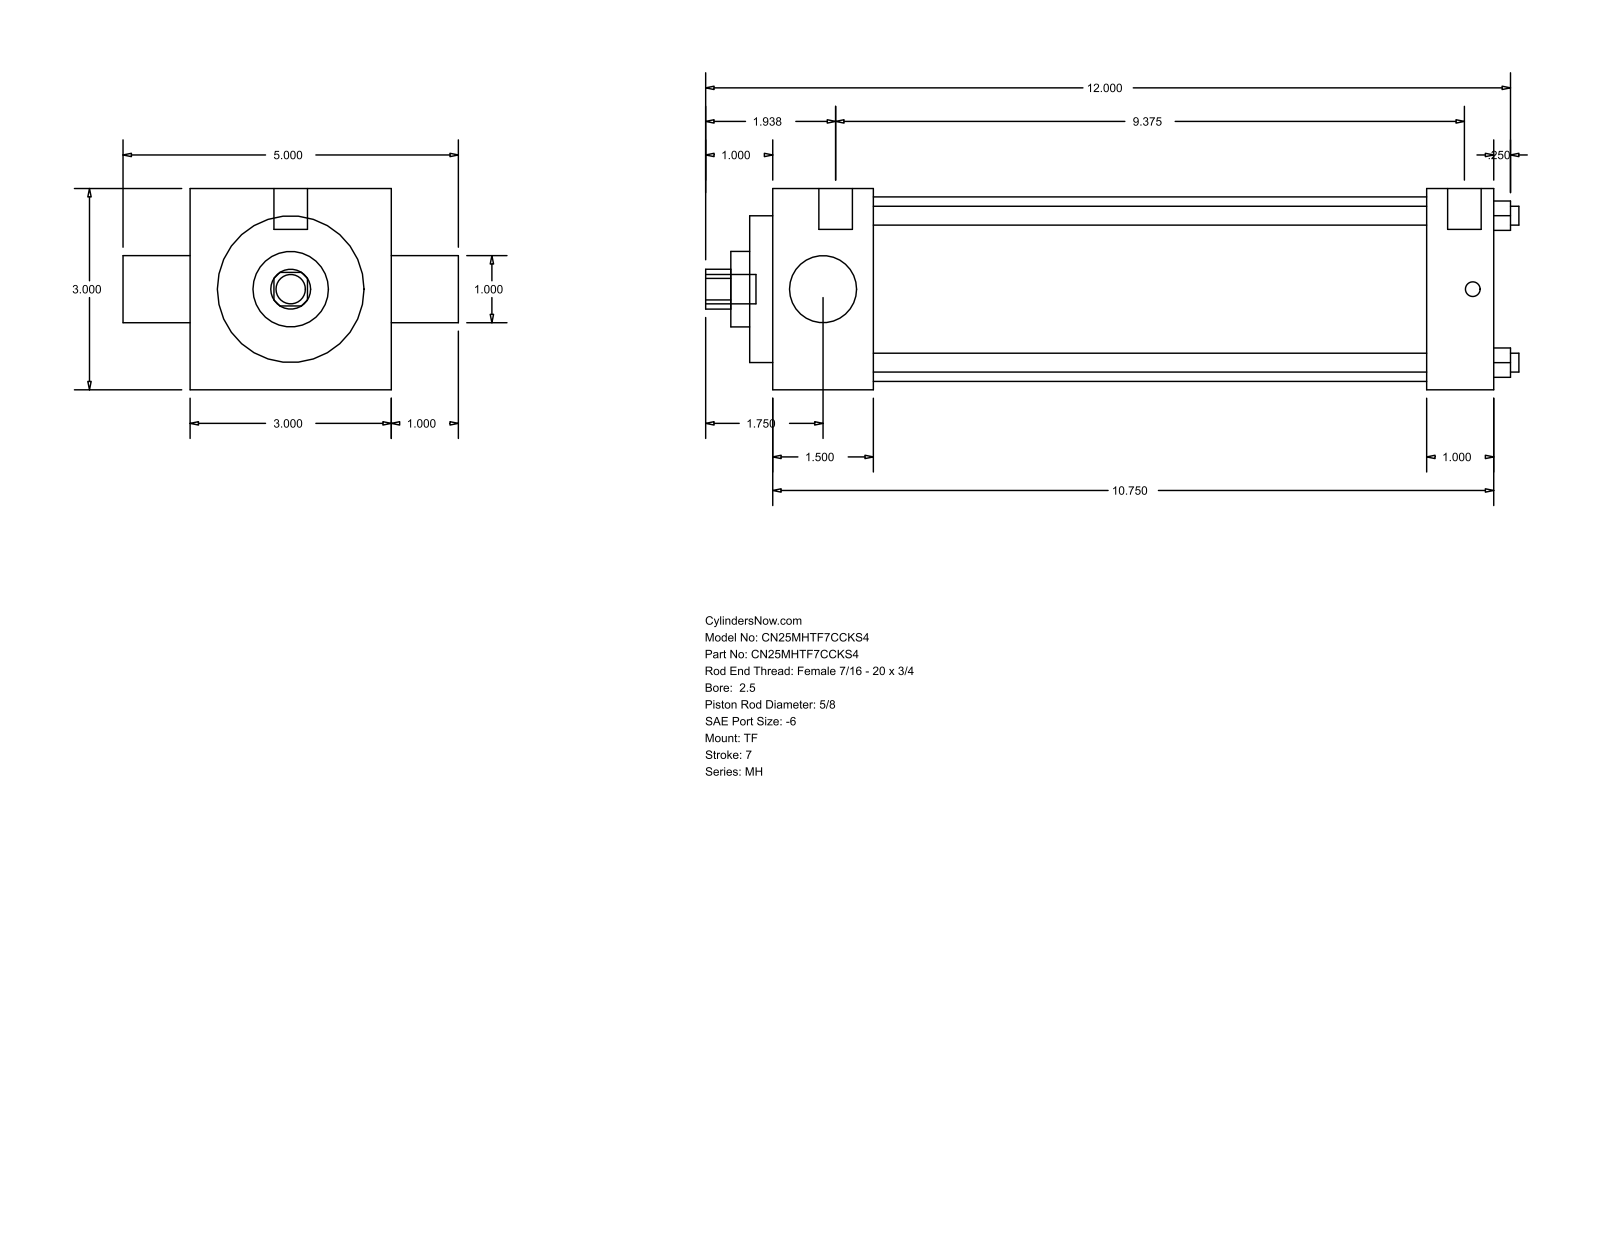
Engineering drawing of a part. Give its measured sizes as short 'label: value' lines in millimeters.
name: MH_TF__0250_0.625
written by: GSSL Pune (CONFIG_CONTROL_DESIGN)
unit: mm
bodies: 0 solids, 86 faces (61 planar, 25 cylindrical, 0 other)
size: 307.98 × 127 × 76.2
holes: 4× ⌀7.14, 1× ⌀15.88, 1× ⌀25.4, 1× ⌀28.57, 1× ⌀55.55, 1× ⌀69.85
bosses: 3× ⌀5.56, 2× ⌀12.7, 1× ⌀11.11
rounds: 1× R7.54
face distances: 76.2, 273.05, 25.4, 38.1, 234.95, 247.65, 209.55, 8.73, 46.83, 256.38
hole spacings: 39.33, 55.62, 78.66
